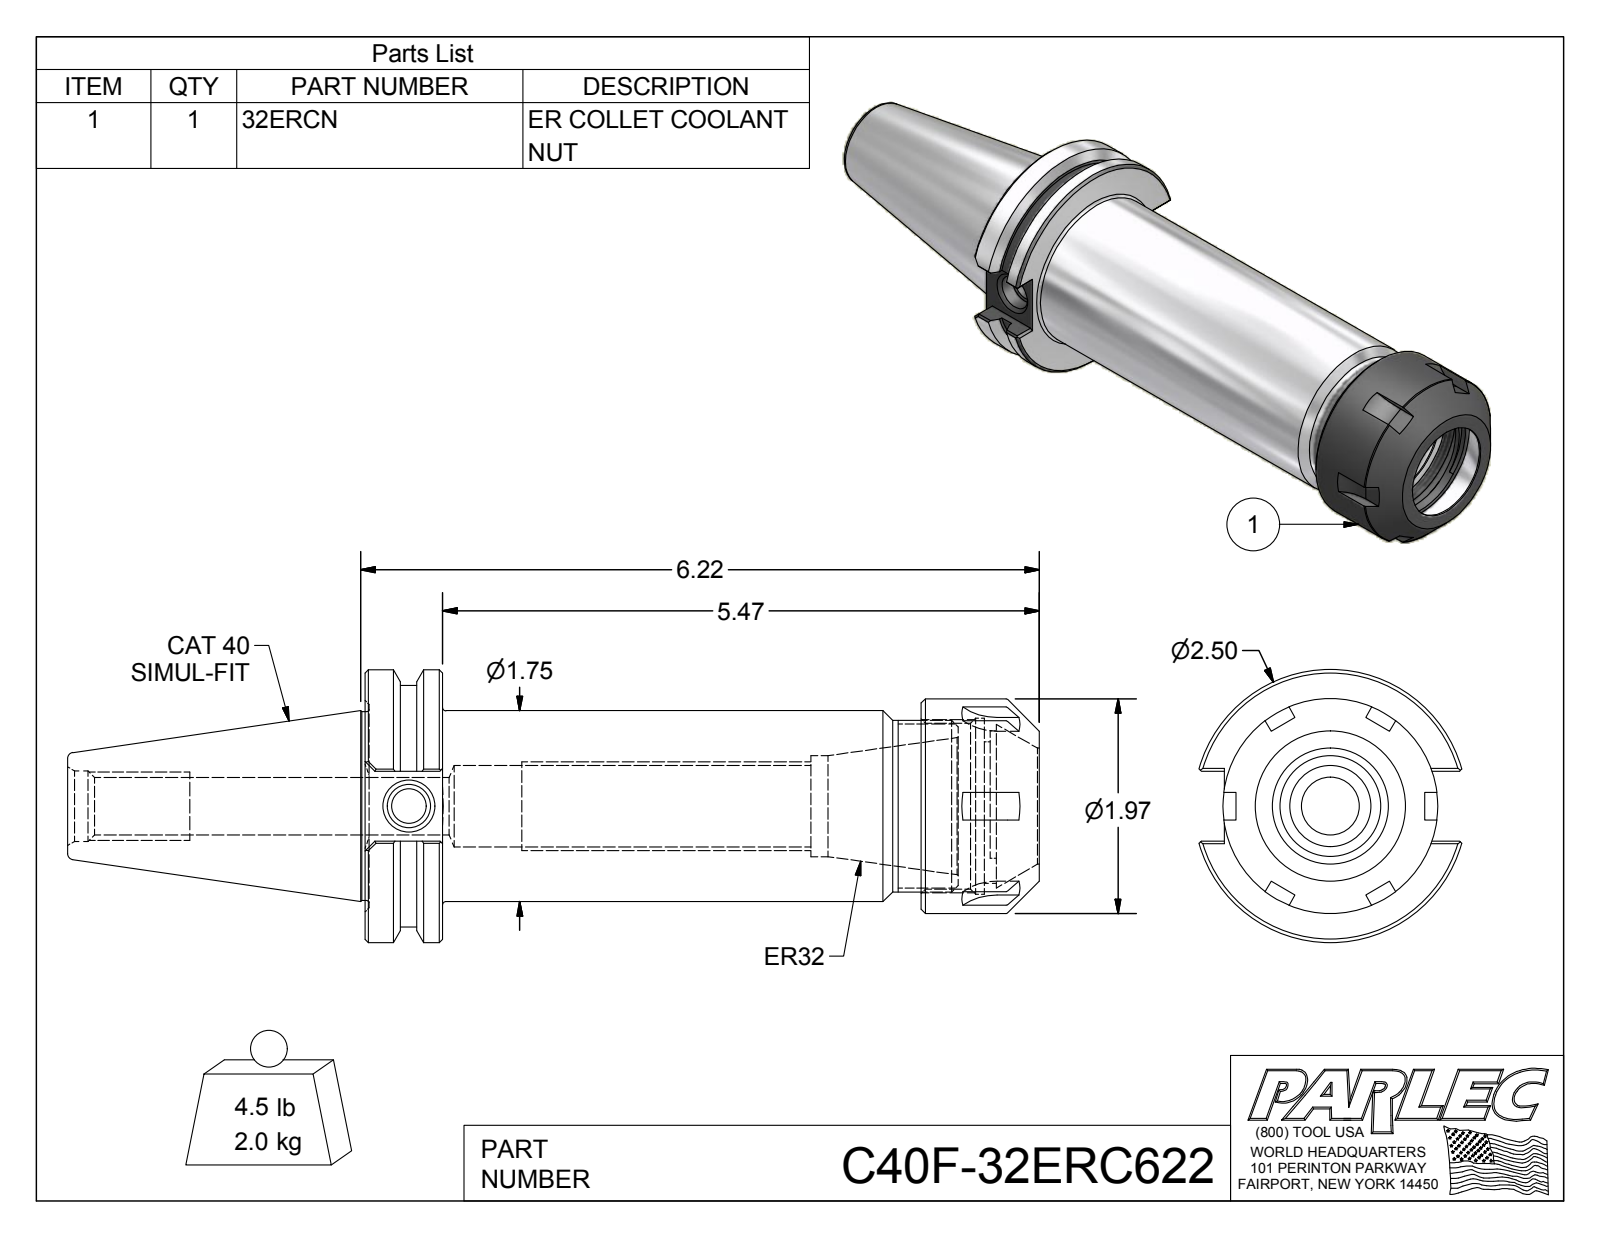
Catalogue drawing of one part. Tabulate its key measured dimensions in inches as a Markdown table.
| quantity | value |
| --- | --- |
| part name | C40F-32ERC622; C40F-32ER6-1; 32ERCN |
| STEP written by | Autodesk Inventor 2012 (AUTOMOTIVE_DESIGN) |
| units | inches |
| bodies | 2 solids, 121 faces (56 planar, 27 cylindrical, 38 other) |
| overall size | 8.908 × 2.5 × 2.406 |
| volume | 15.9 in³ |
| surface area | 84.15 in² |
| round holes (diameter × count) | 0.315 × 1, 0.399 × 1, 0.527 × 1, 0.648 × 1, 0.745 × 1, 0.925 × 1, 1.063 × 1, 1.299 × 1, 1.522 × 1, 1.614 × 1 |
| round bosses / shafts (diameter × count) | 2.5 × 1, 2.215 × 1, 1.969 × 1, 1.75 × 1, 1.73 × 1, 1.575 × 1 |
| partial cylindrical surfaces (radius × count) | 0.5 × 6, 0.689 × 1 |
| main face-to-face distances | 0.711, 5.098, 4.387, 5.677, 4.966, 0.579, 6.181, 5.47, 1.083, 0.504 |
| hole center spacings | 0.059 |
